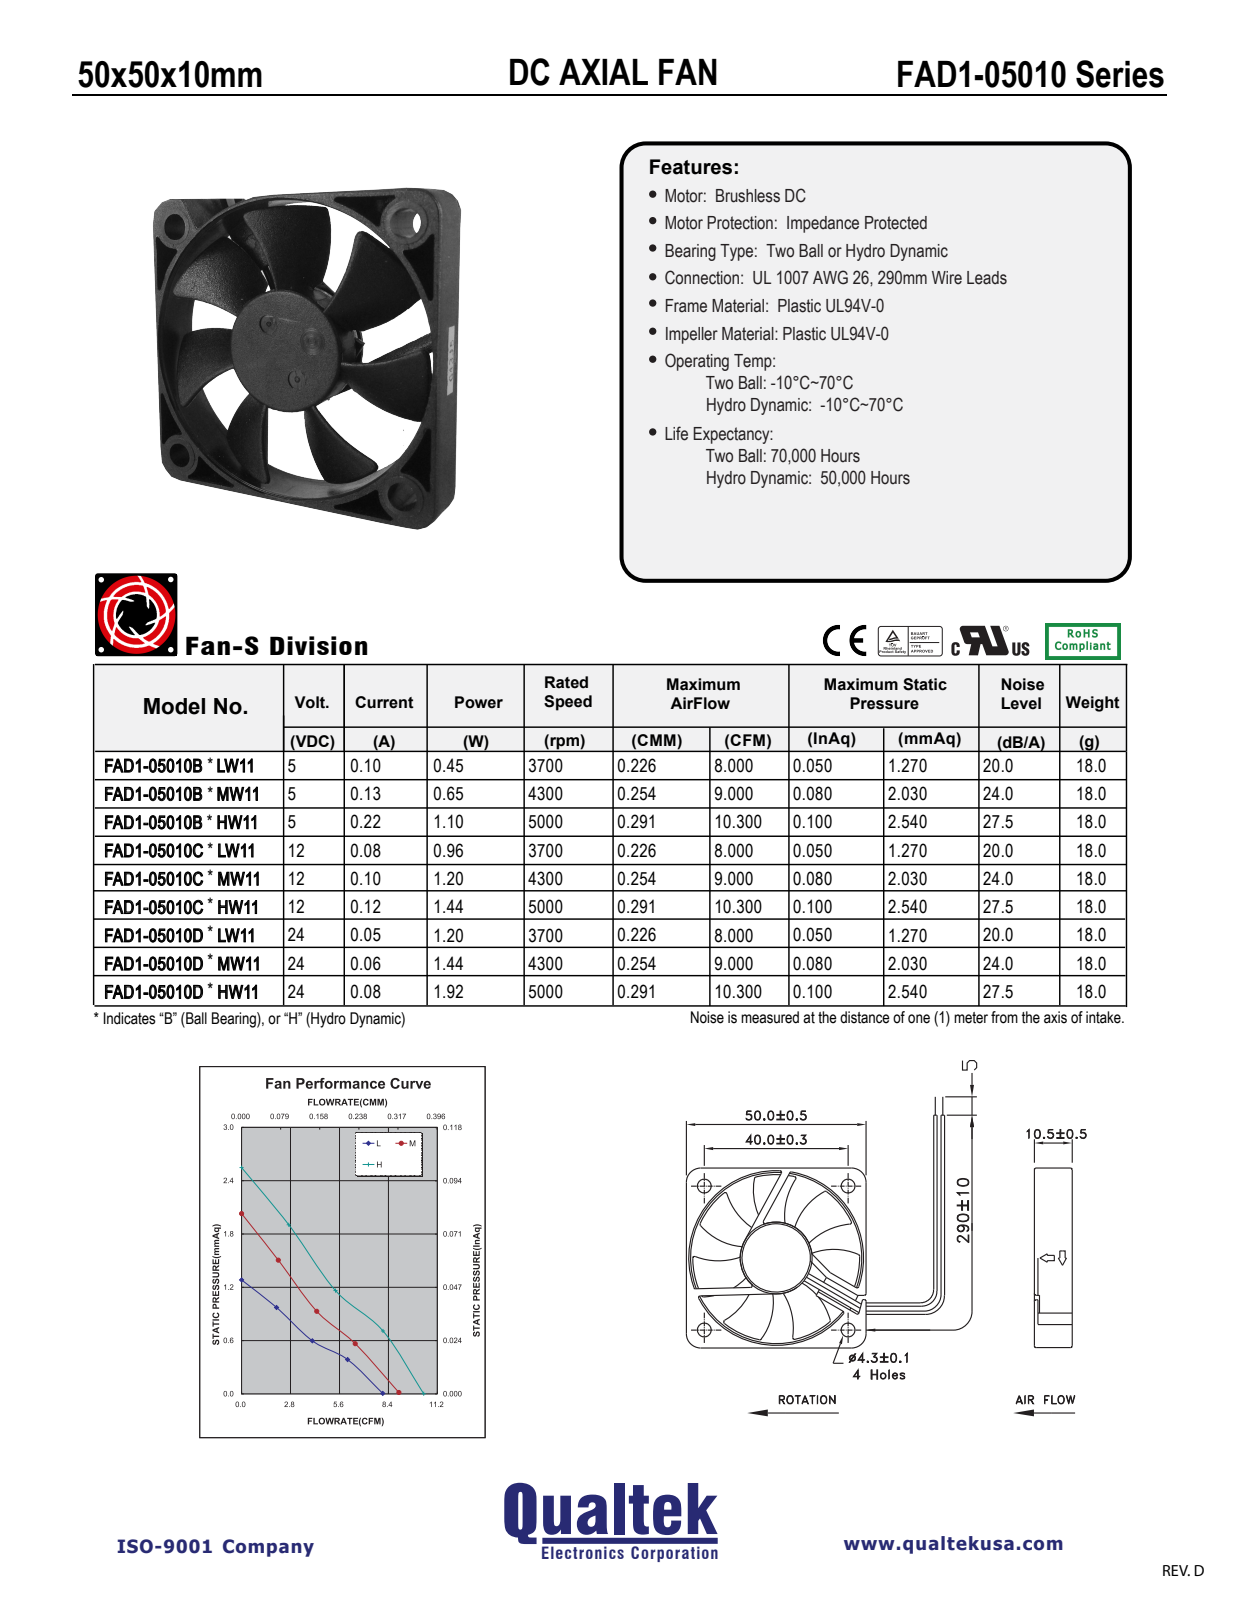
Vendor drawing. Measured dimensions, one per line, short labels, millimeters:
name: 230FR05010AXXXXX-B
written by: PRO/ENGINEER BY PARAMETRIC TECHNOLOGY CORPORATION, 2012360 (CONFIG_CONTROL_DESIGN)
unit: mm
bodies: 1 solid, 222 faces (73 planar, 113 cylindrical, 36 other)
size: 50.2 × 50 × 10.5
volume: 5 683 mm³; area: 7 975 mm²
holes: 4× ⌀4.3, 4× ⌀6, 2× ⌀2.5, 1× ⌀4, 1× ⌀5.01, 1× ⌀5.05, 1× ⌀18, 1× ⌀47.6
bosses: 1× ⌀6.8, 1× ⌀6.03
rounds: 42× R0.5, 4× R0.25, 4× R4, 3× R1, 2× R3.81, 2× R3.81, 1× R1.25, 1× R3.81
face distances: 50, 1.19, 48.81, 1.1, 1.2, 10.5, 9.3, 1.3, 10.4, 47.62
hole spacings: 28.28, 40, 56.57, 4.97, 5.03, 10, 23.62, 23.68
